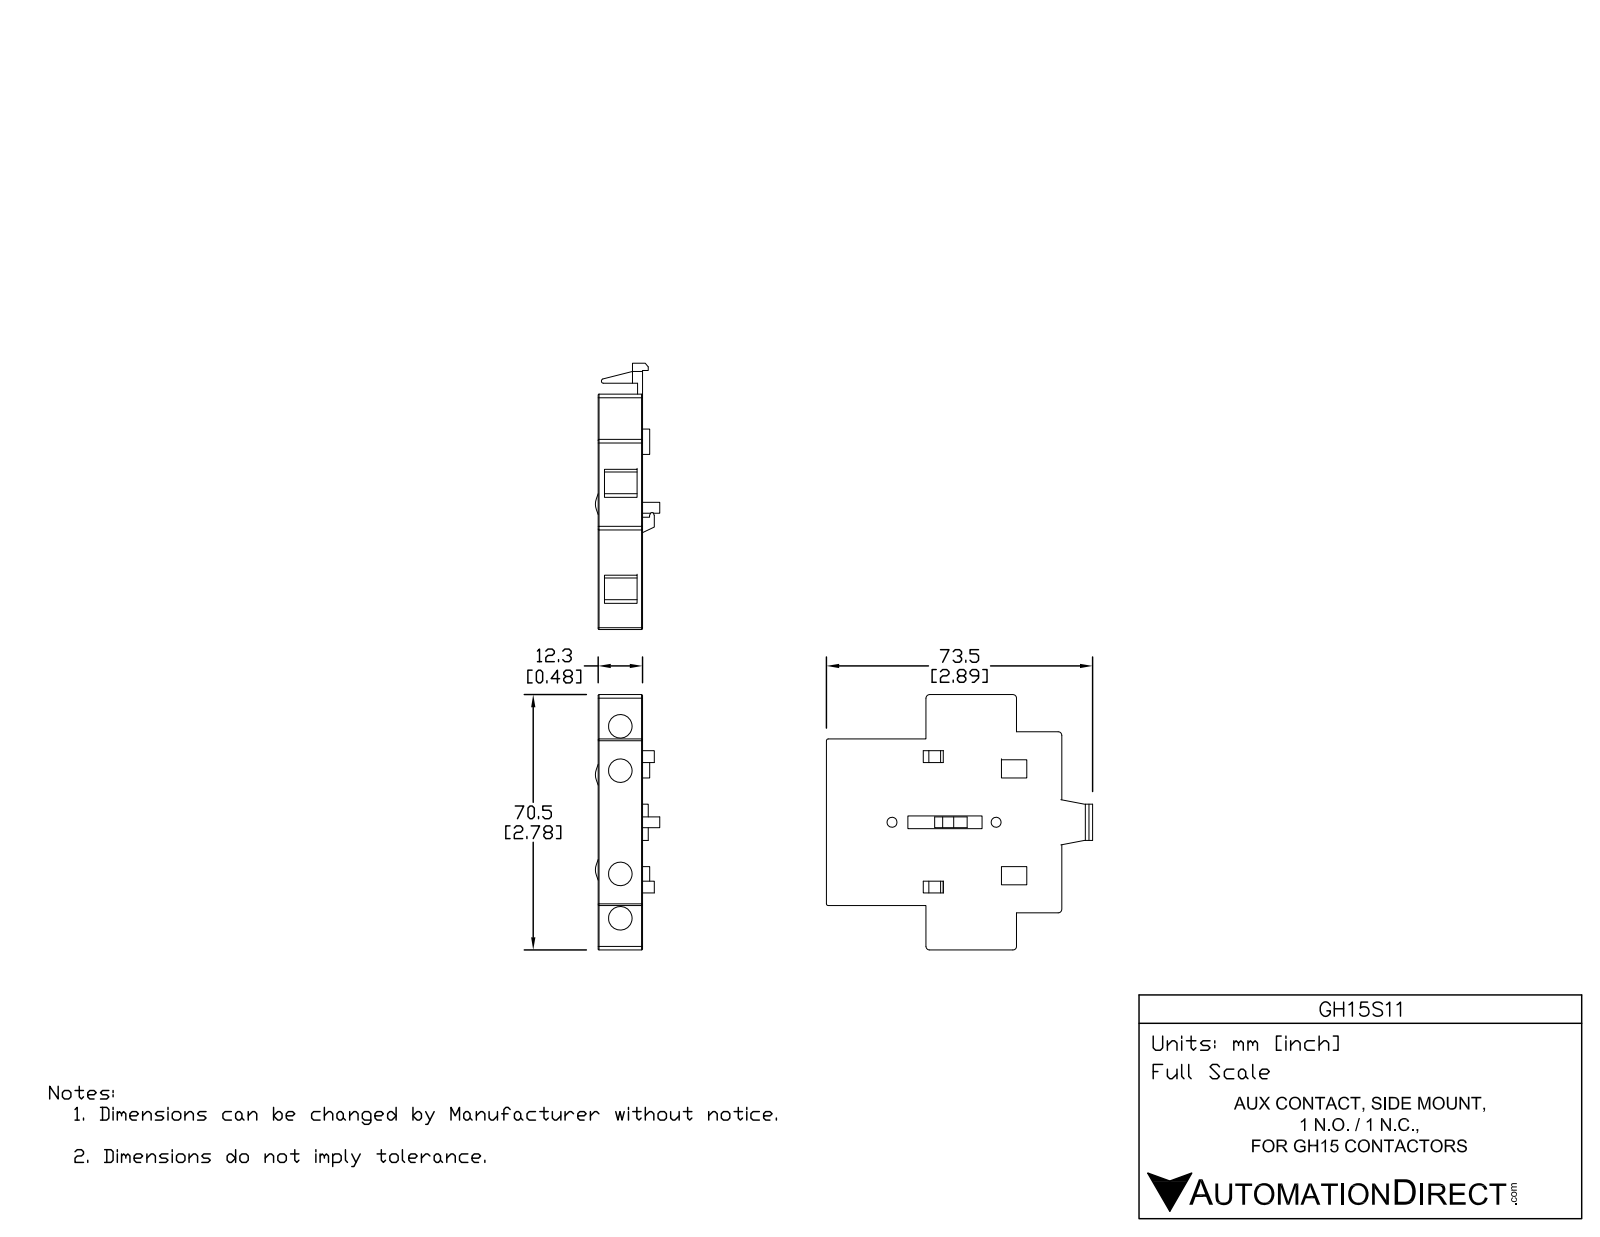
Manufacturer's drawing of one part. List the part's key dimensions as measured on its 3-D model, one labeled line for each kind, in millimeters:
Part name (STEP PRODUCT): GH15S11
STEP written by: SolidWorks 2009 (CONFIG_CONTROL_DESIGN)
Units: millimetres
Bodies: 1 solid, 206 faces (133 planar, 55 cylindrical, 18 other)
Overall size (bounding box): 73.52 × 70.5 × 17.75
Volume: 40 304 mm³ · Surface area: 14 505 mm²
Round holes (diameter × count): ⌀6.5 ×4, ⌀2.75 ×2, ⌀7.25 ×2
Round bosses / shafts (diameter × count): ⌀7 ×2
Partial cylindrical surfaces — rounded edges, fillets, slot ends (radius × count): R0.25 ×20, R1 ×6, R0.5 ×4
Main face-to-face distances: 12.25, 10.75, 10.5, 2, 65, 9, 58.25, 12.5, 1.75, 23.25
Hole centre spacings: 12.25, 40.75, 17.95, 17.96, 21.08, 21.09, 26.25, 28.5
